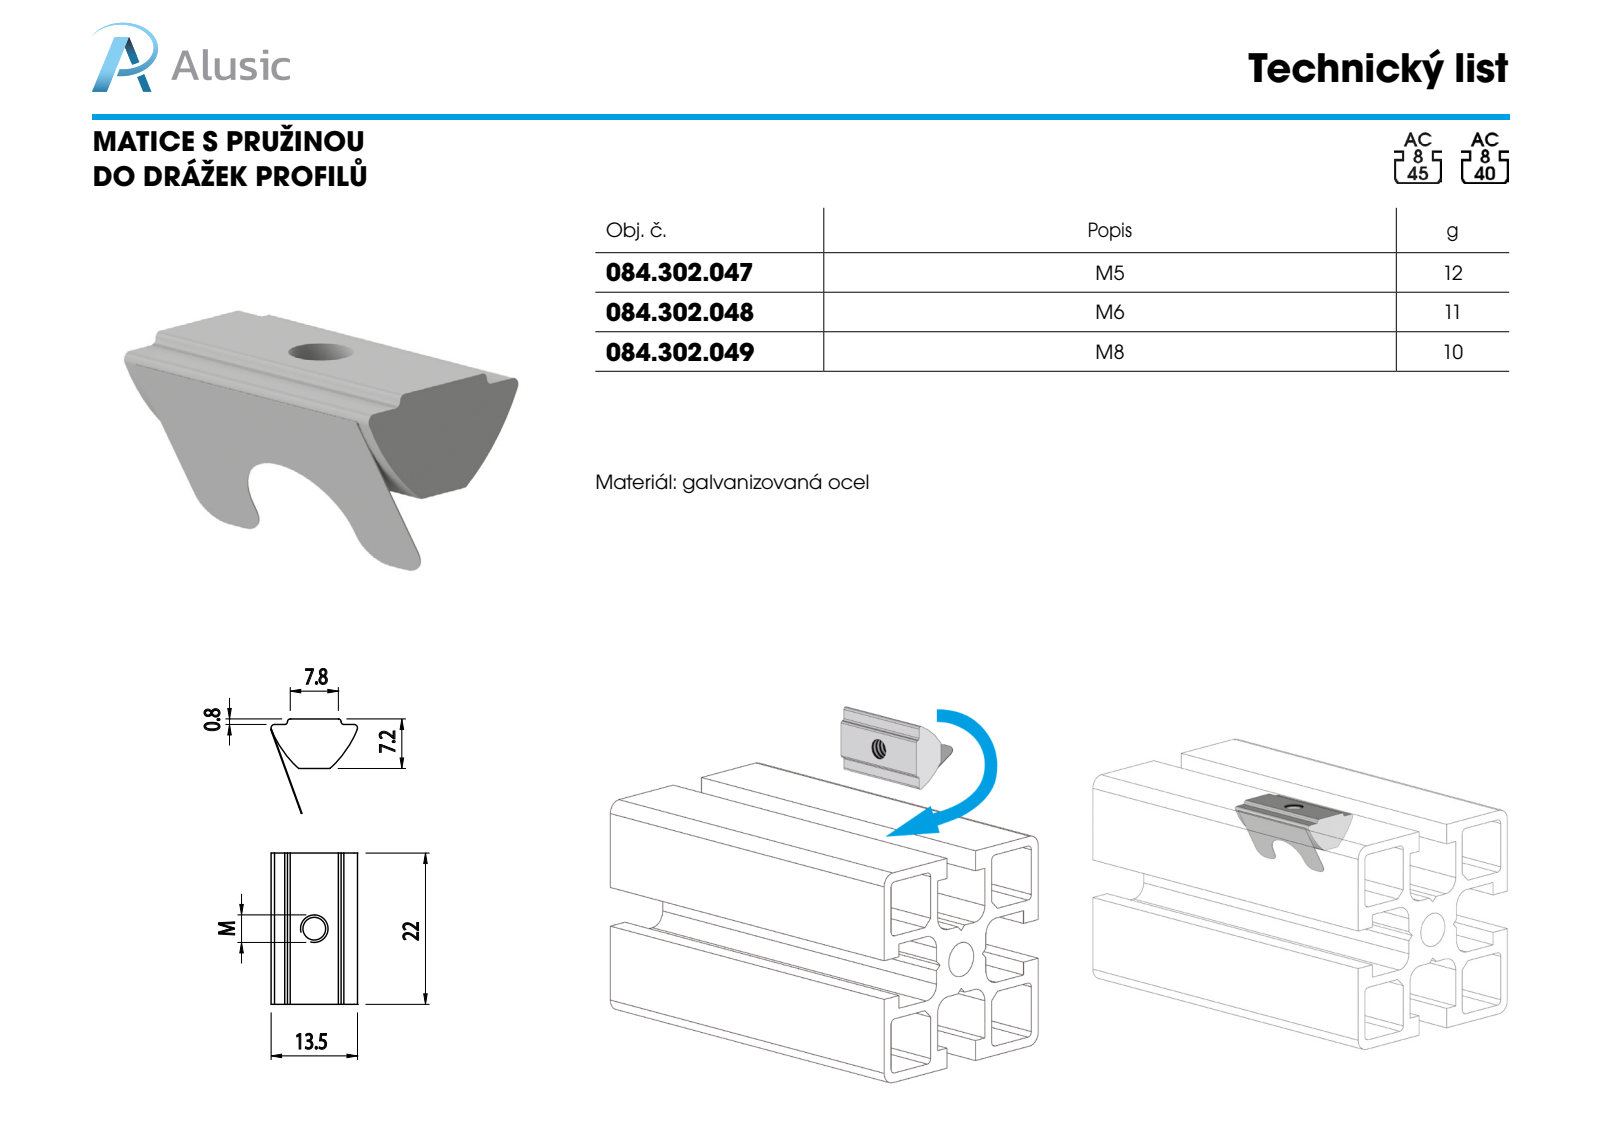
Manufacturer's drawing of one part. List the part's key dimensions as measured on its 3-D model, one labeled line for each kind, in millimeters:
Part name (STEP PRODUCT): 084.302.049
STEP written by: SolidWorks 2011 (CONFIG_CONTROL_DESIGN)
Units: millimetres
Bodies: 1 solid, 34 faces (15 planar, 17 cylindrical, 2 other)
Overall size (bounding box): 22 × 13.57 × 12.76
Volume: 1 295 mm³ · Surface area: 1 302 mm²
Round holes (diameter × count): ⌀6.8 ×1
Partial cylindrical surfaces — rounded edges, fillets, slot ends (radius × count): R0.4 ×4, R2 ×4, R0.5 ×2, R15 ×2, R4.5 ×1
Main face-to-face distances: 0.8, 6.4, 7.2, 20, 13, 5.5, 14.5, 9
